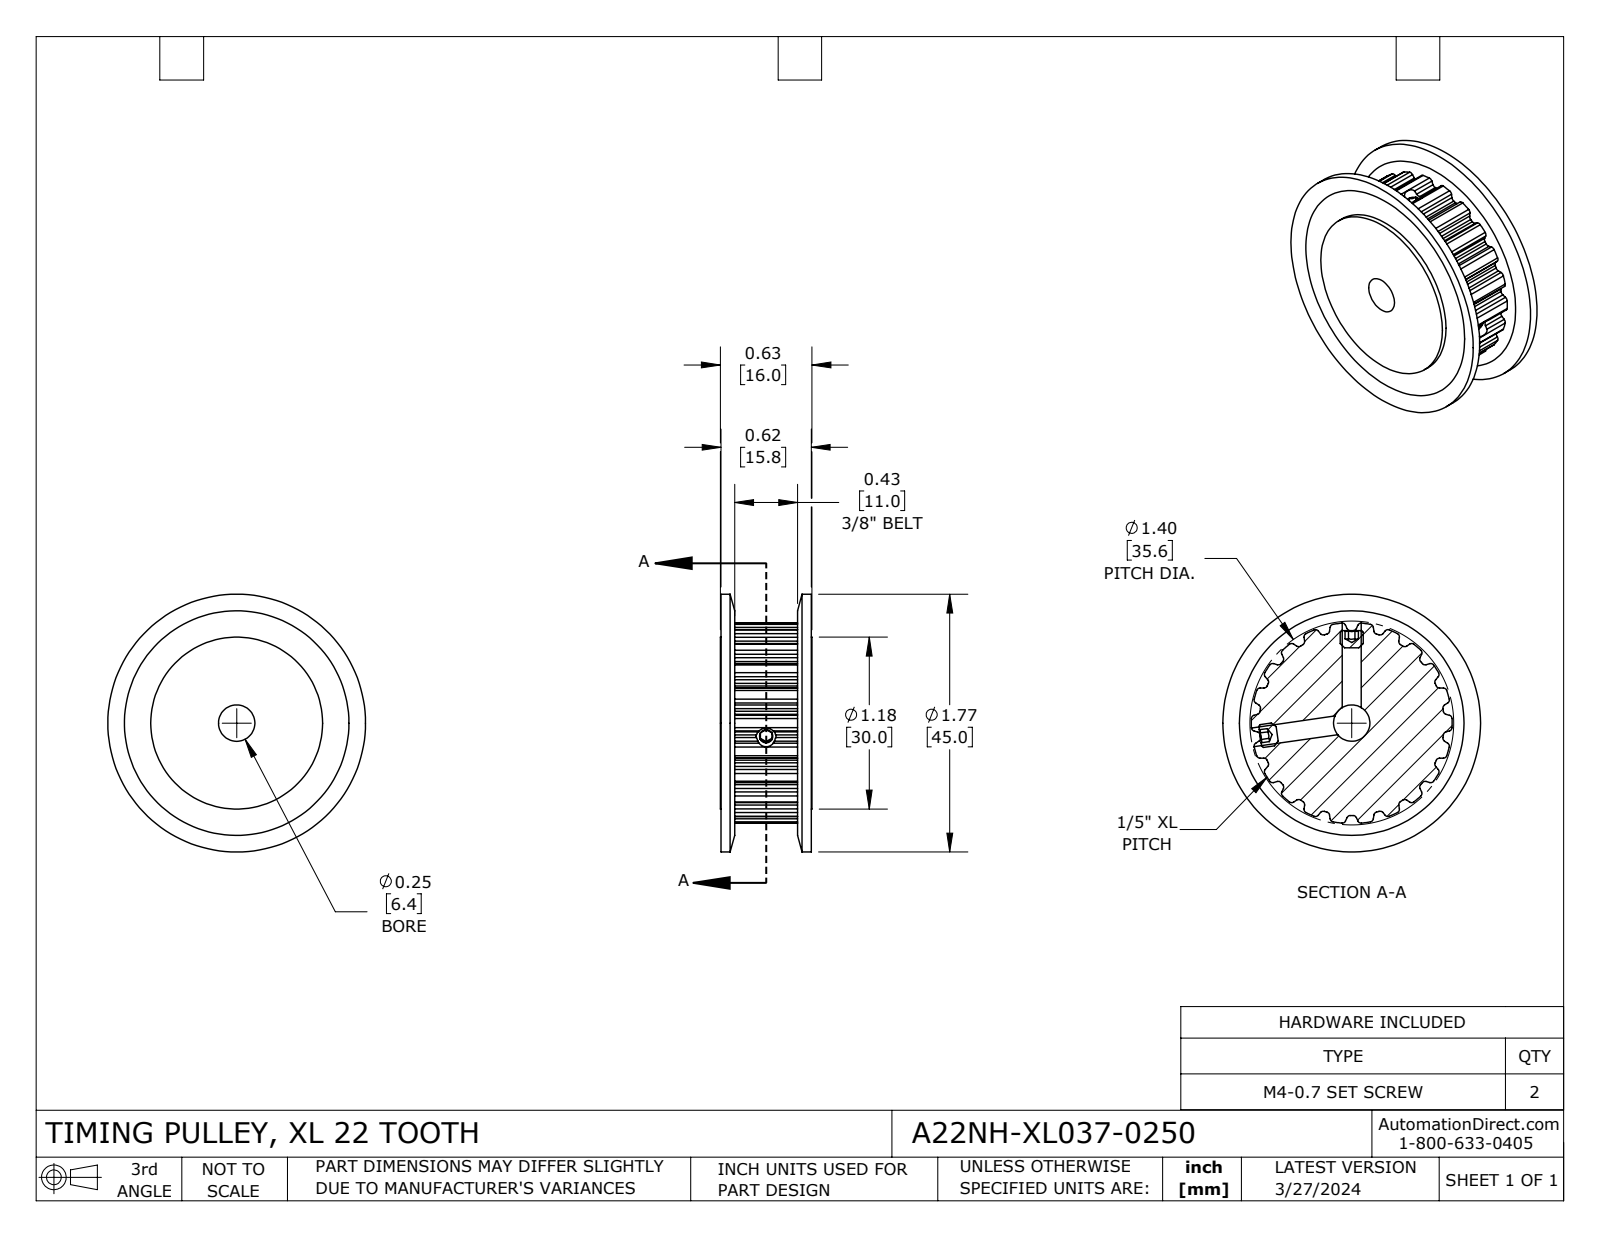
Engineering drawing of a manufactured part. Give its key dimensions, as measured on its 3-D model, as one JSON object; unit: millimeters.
{"part_name": "A22NH-XL037-0250", "step_written_by": "SolidWorks 2021 (CONFIG_CONTROL_DESIGN)", "units": "millimeters", "bodies": {"solids": 5, "faces": 284, "planar": 72, "cylindrical": 178, "other": 34}, "overall_size": [45, 45, 16], "volume_mm3": 15657, "surface_area_mm2": 8797, "round_holes": [[3.3, 2], [6.35, 1], [30, 1]], "round_bosses_or_shafts": [[4, 2], [45, 1]], "partial_cylinders_radius": [[0.61, 88], [16.14, 1], [17.54, 1]], "face_to_face_distances": [2.5, 13.5, 0.9, 15.1, 1.6, 12.6, 11, 16, 14.2, 12.48]}
